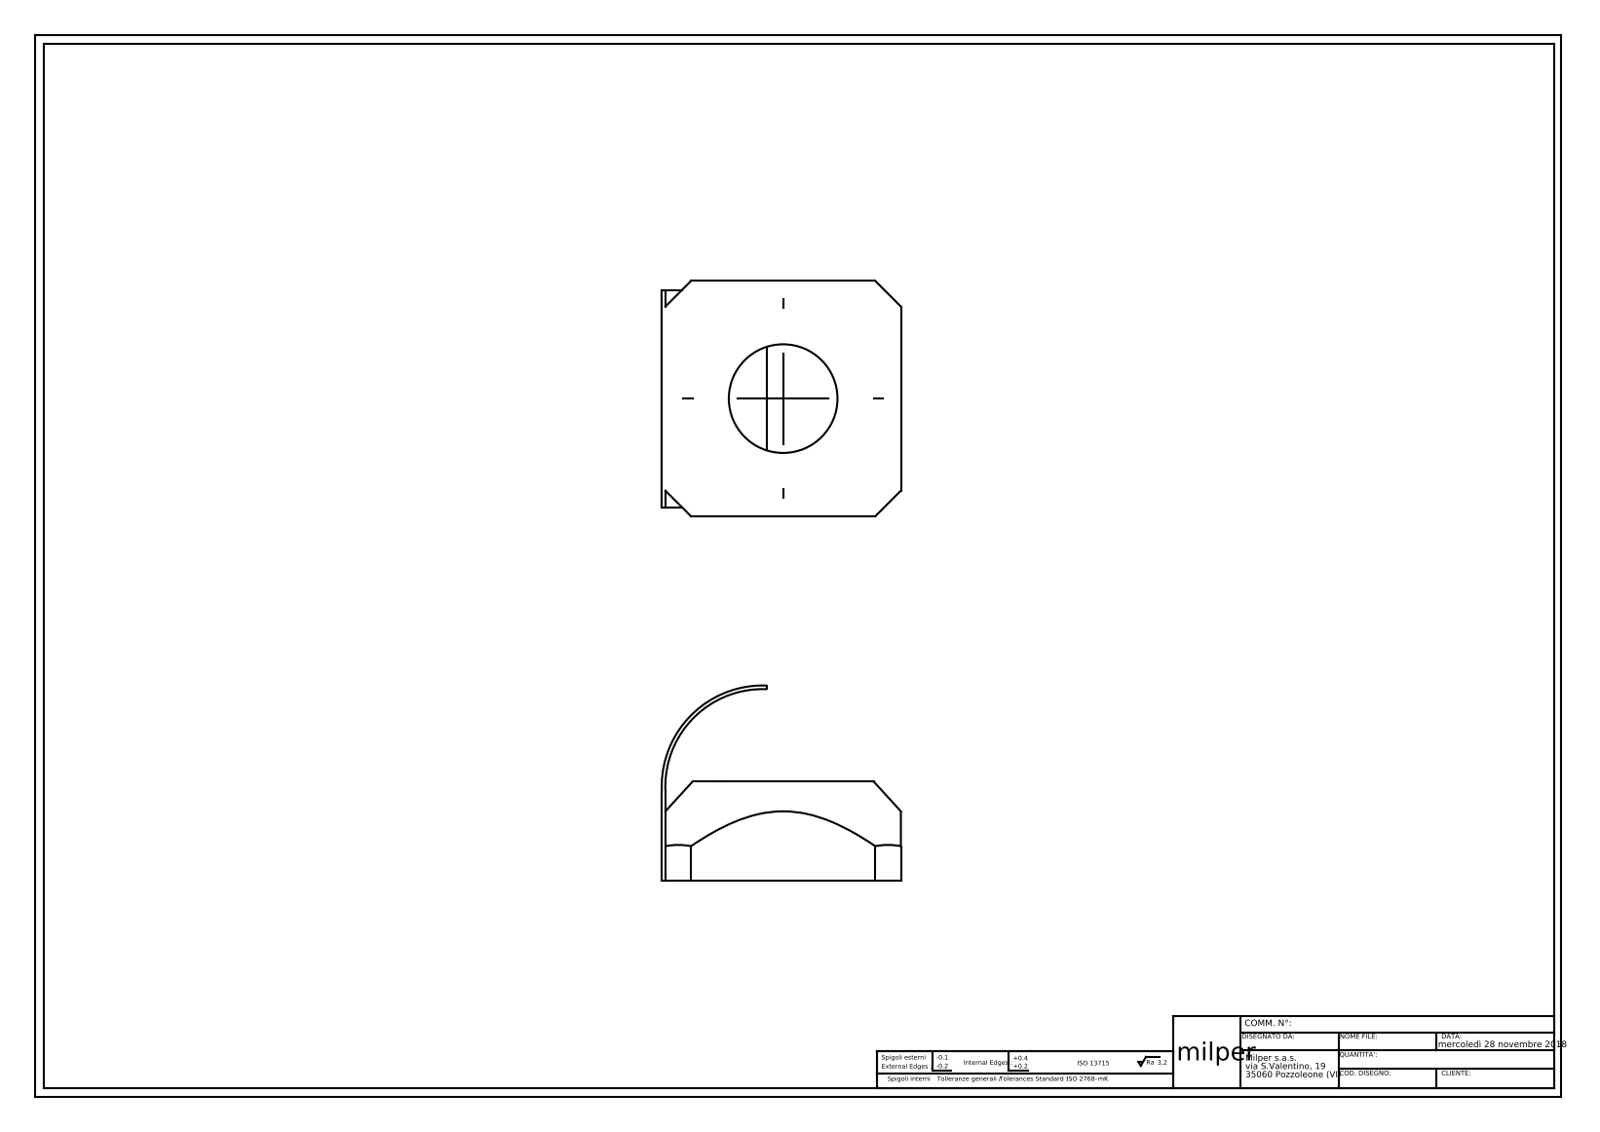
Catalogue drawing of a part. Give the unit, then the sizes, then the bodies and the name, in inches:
Units: inches
Overall size (bounding box): 0.52 × 0.512 × 0.425
Round holes (diameter × count): ⌀0.236 ×1
Partial cylindrical surfaces — rounded edges, fillets, slot ends (radius × count): R0.079 ×2, R0.211 ×1, R0.219 ×1
Main face-to-face distances: 0.512, 0.217, 0.52, 0.645, 0.02, 0.492, 0.472, 0.291, 0.22, 0.228
Volume: 0.04 in³ · Surface area: 1.31 in²
Bodies: 1 solid, 24 faces (14 planar, 8 cylindrical, 2 other)
Part name (STEP PRODUCT): dado-M6-molla-3D
STEP written by: SolidWorks 2018 (CONFIG_CONTROL_DESIGN)
